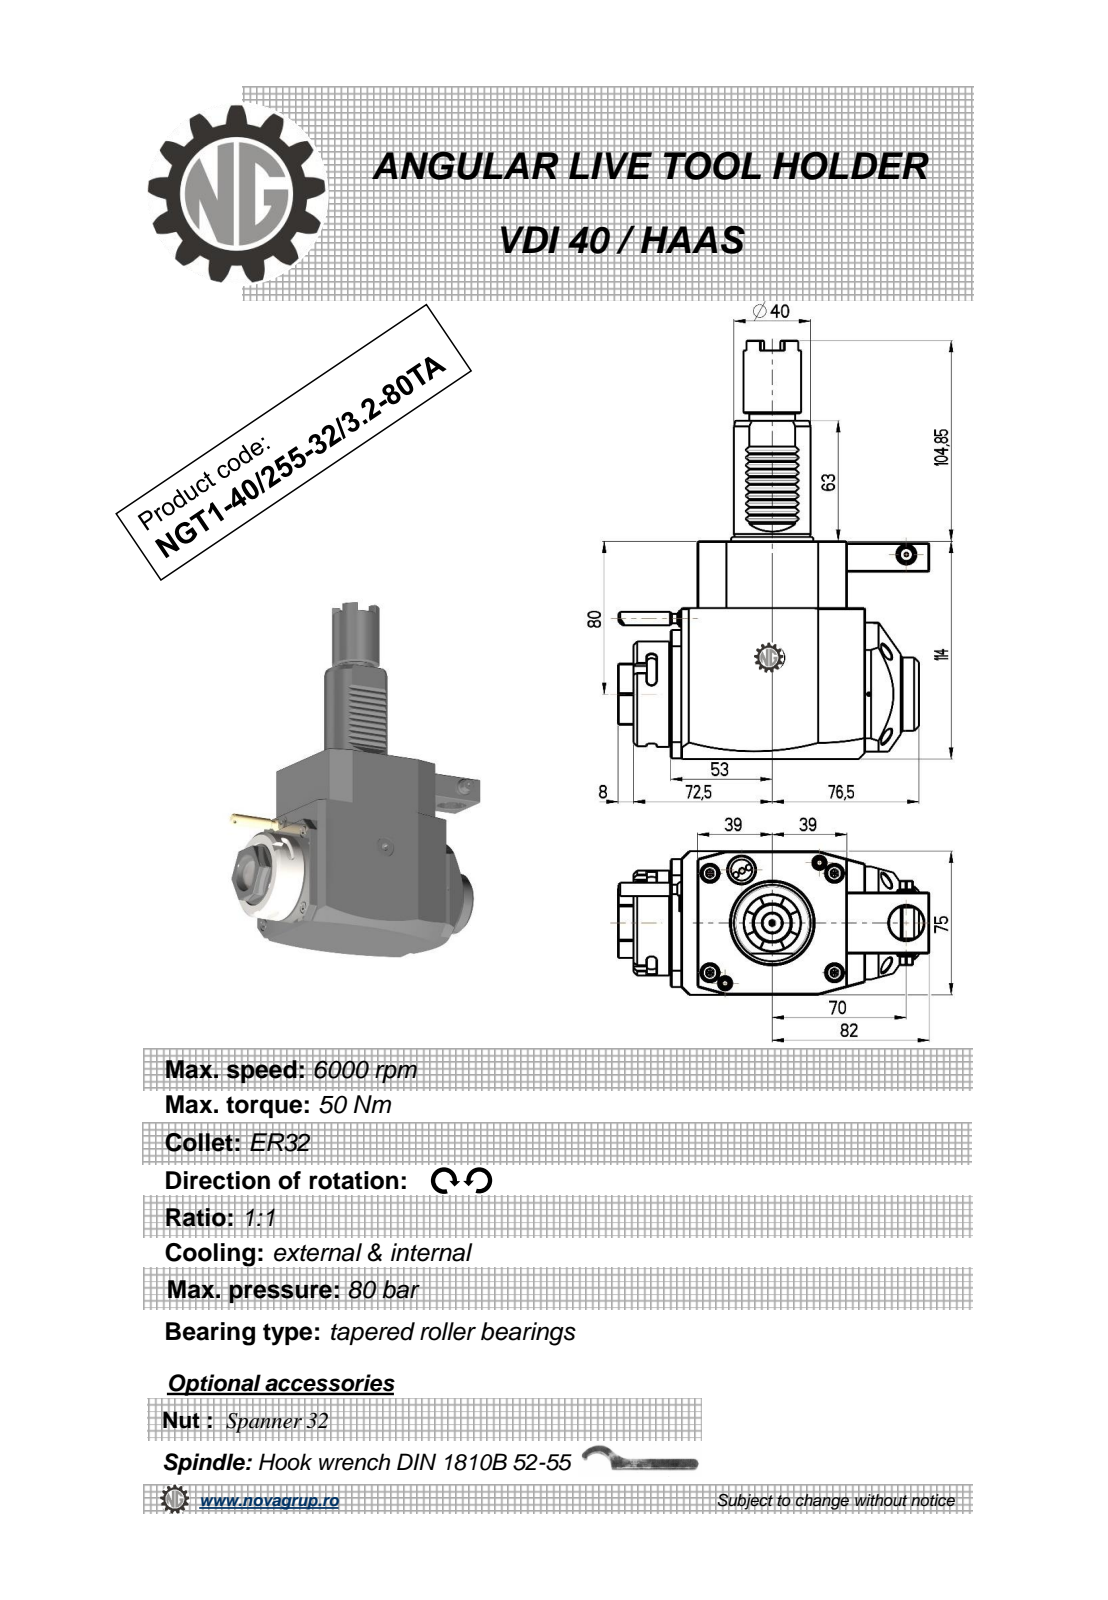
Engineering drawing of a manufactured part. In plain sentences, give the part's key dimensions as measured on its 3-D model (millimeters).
The part is named "NGT1_40_255_32_3_2_80TA". Its 3-D file was written by "PRO/ENGINEER BY PARAMETRIC TECHNOLOGY CORPORATION, 2010280 (CONFIG_CONTROL_DESIGN)". It is 1 solid with 395 faces: 219 planar, 88 cylindrical and 88 other. Overall it measures 218.85 by 162.5 by 75 millimeters. Its volume is 1 006 000 cubic millimeters and its surface area 78 611 square millimeters. Round holes: 1 of diameter 2, 1 of diameter 2.5, 1 of diameter 3, 1 of diameter 9.5, 1 of diameter 18, 1 of diameter 23. Round bosses or shafts: 2 of diameter 8.96, 1 of diameter 55, 1 of diameter 48, 1 of diameter 40, 1 of diameter 38.5, 1 of diameter 30, 1 of diameter 20, 1 of diameter 10. Partial cylindrical surfaces (rounded edges, fillets, slot ends): 10 of radius 0.3, 6 of radius 2.5, 2 of radius 180, 1 of radius 0.5, 1 of radius 3.85, 1 of radius 4.25, 1 of radius 24.5, 1 of radius 37.5. The main face-to-face distances are 75, 114, 14, 79, 33.5, 92, 78, 98, 21.5, 19.5. The hole center spacings are 37.35, 43.2, 72.5.
